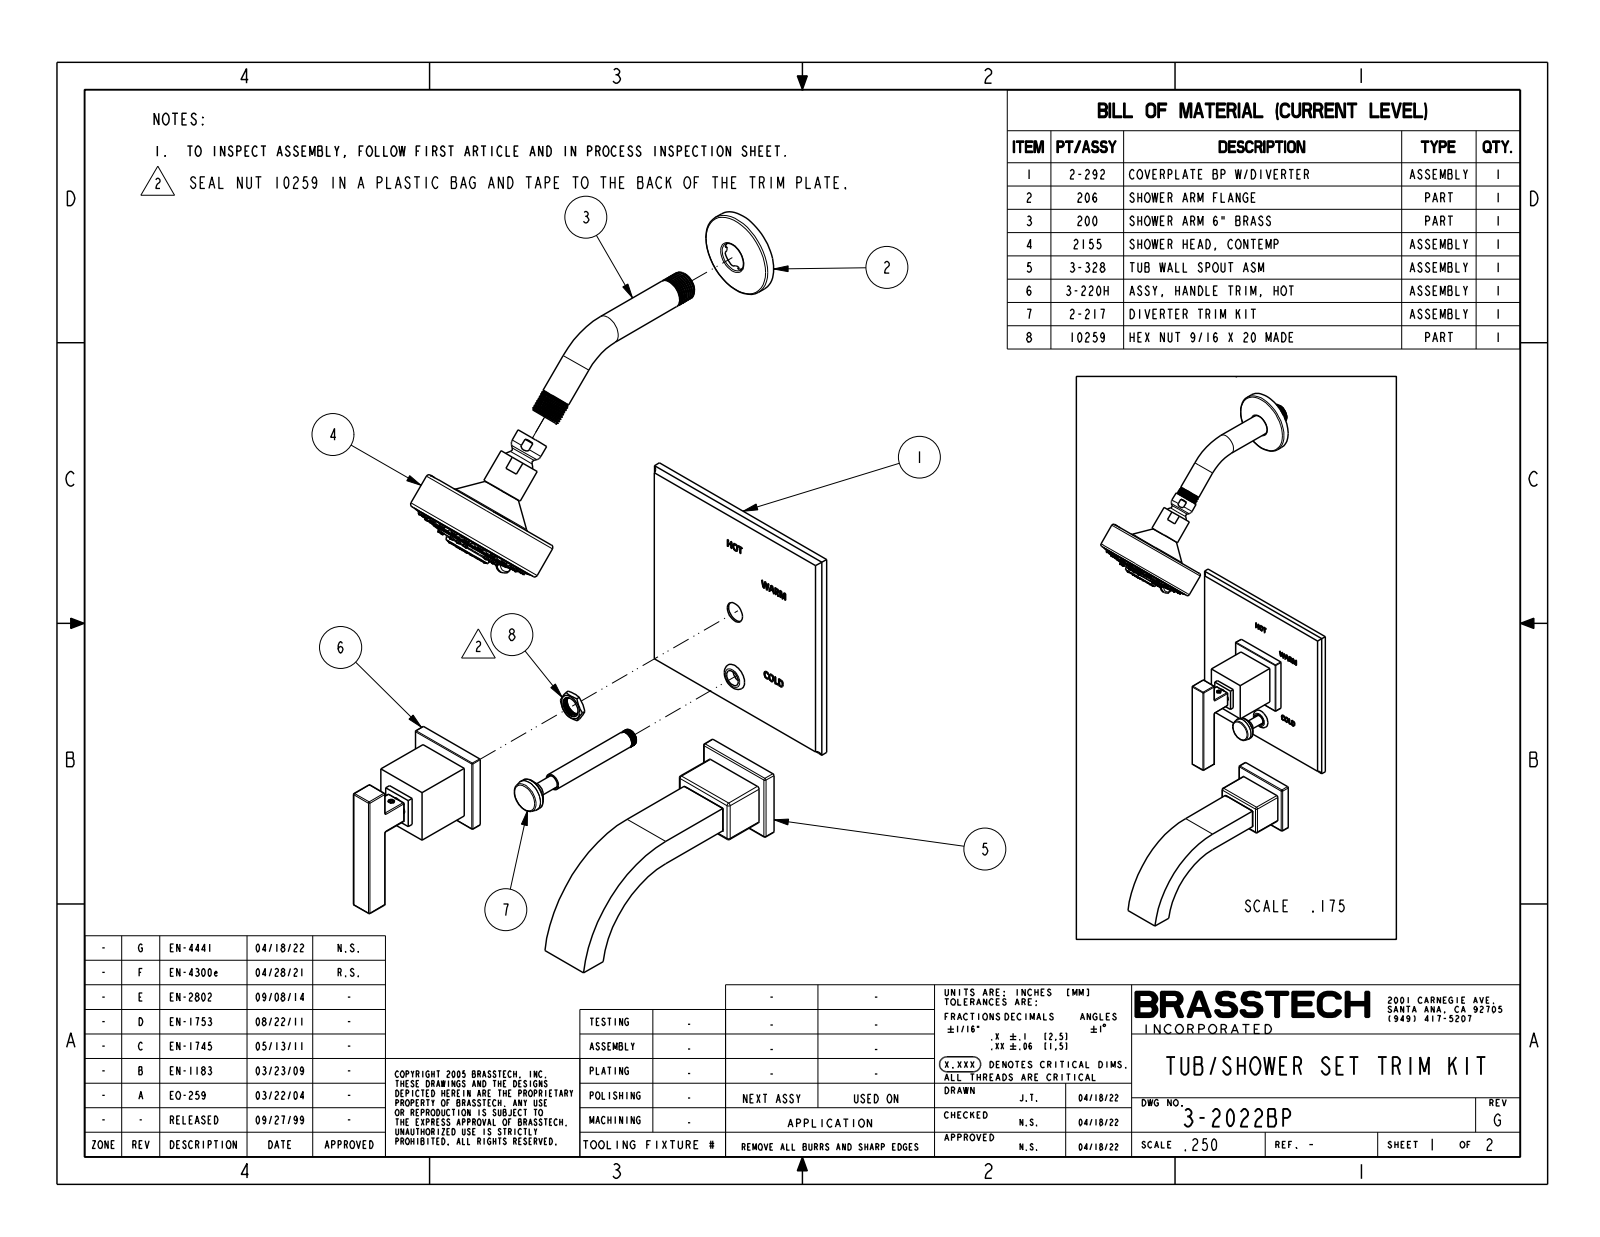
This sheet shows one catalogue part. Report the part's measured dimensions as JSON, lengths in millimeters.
{"part_name": "3-2022BP", "step_written_by": "CREO PARAMETRIC BY PTC INC, 2018400 (CONFIG_CONTROL_DESIGN)", "units": "millimeters", "bodies": {"solids": 3, "faces": 1358, "planar": 279, "cylindrical": 254, "other": 825}, "overall_size": [549.8, 207.6, 165.1], "volume_mm3": 867400, "surface_area_mm2": 155600, "round_holes": [[1.5, 8], [23.5, 1]], "round_bosses_or_shafts": [[3.6, 39], [4.2, 23], [20.7, 2], [101.6, 1], [94.6, 1], [60.5, 1], [59, 1], [29.2, 1]], "partial_cylinders_radius": [[0.8, 22], [0.5, 8], [1, 8], [1.5, 8], [2, 8], [3.2, 4], [0.5, 2], [3.5, 1]], "face_to_face_distances": [8, 12.4, 28.3, 1.3, 40.6, 39.4, 11.1, 27, 62.2, 102.9], "hole_center_spacings": [11.3, 14.7, 20.8, 20.8, 27.2, 11.3, 14.7, 27.2]}
